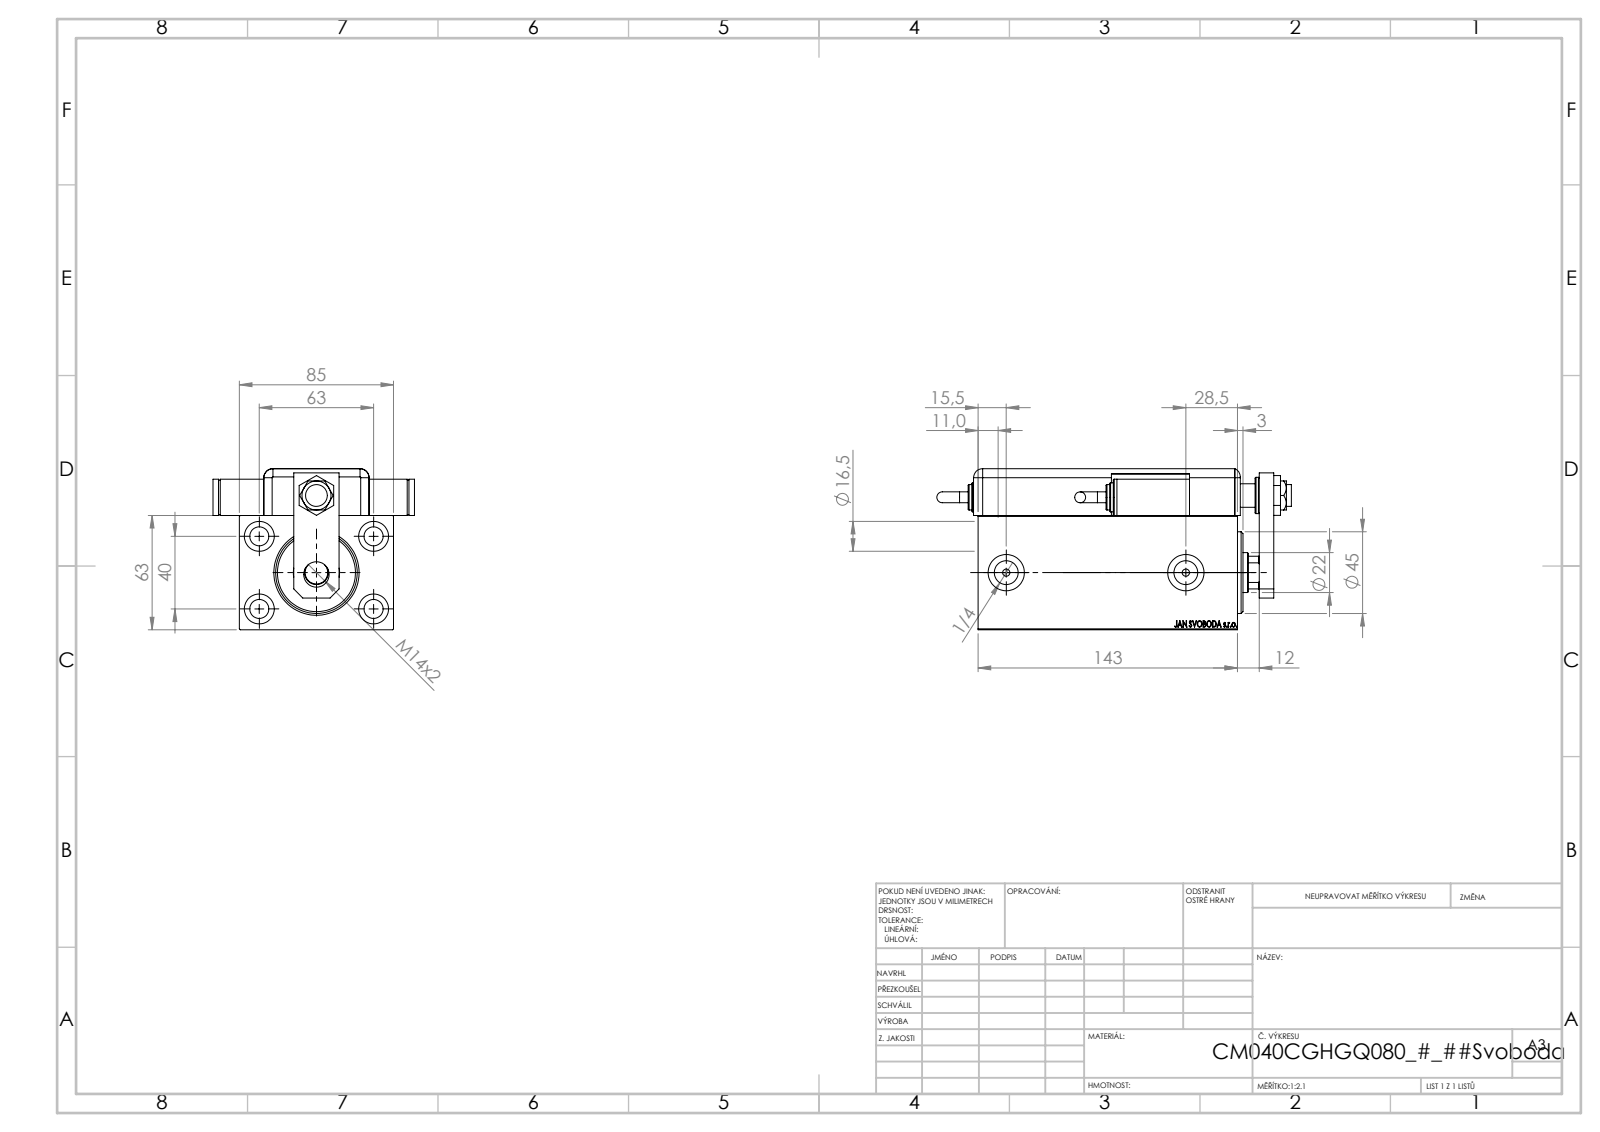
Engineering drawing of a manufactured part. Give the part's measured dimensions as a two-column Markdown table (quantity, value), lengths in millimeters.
| quantity | value |
| --- | --- |
| part name | SWITCH Q; NUT_D13; V450CM_C_VCP; TYC (+7 more) |
| STEP written by | SolidWorks 2019 (CONFIG_CONTROL_DESIGN) |
| units | millimeters |
| bodies | 13 solids, 1246 faces (614 planar, 115 cylindrical, 517 other) |
| overall size | 195.46 × 111 × 88.8 |
| volume | 795 157 mm³ |
| surface area | 175 639 mm² |
| round holes (diameter × count) | 4 × 4, 10.5 × 4, 16.5 × 4, 8 × 2, 13.16 × 2, 14 × 2, 20 × 2, 12 × 1, 12.5 × 1, 13 × 1, 22 × 1, 25.5 × 1 |
| round bosses / shafts (diameter × count) | 20 × 3, 16 × 2, 14 × 2, 6 × 2 |
| partial cylindrical surfaces (radius × count) | 5 × 9, 10 × 1, 10.5 × 1 |
| main face-to-face distances | 3, 63, 85, 13.5, 25.8, 88.8, 16.5, 12, 85.8, 22.8 |
| hole center spacings | 37.31, 36.79, 37.86, 38.71, 40, 63, 69.99, 74.63 |
